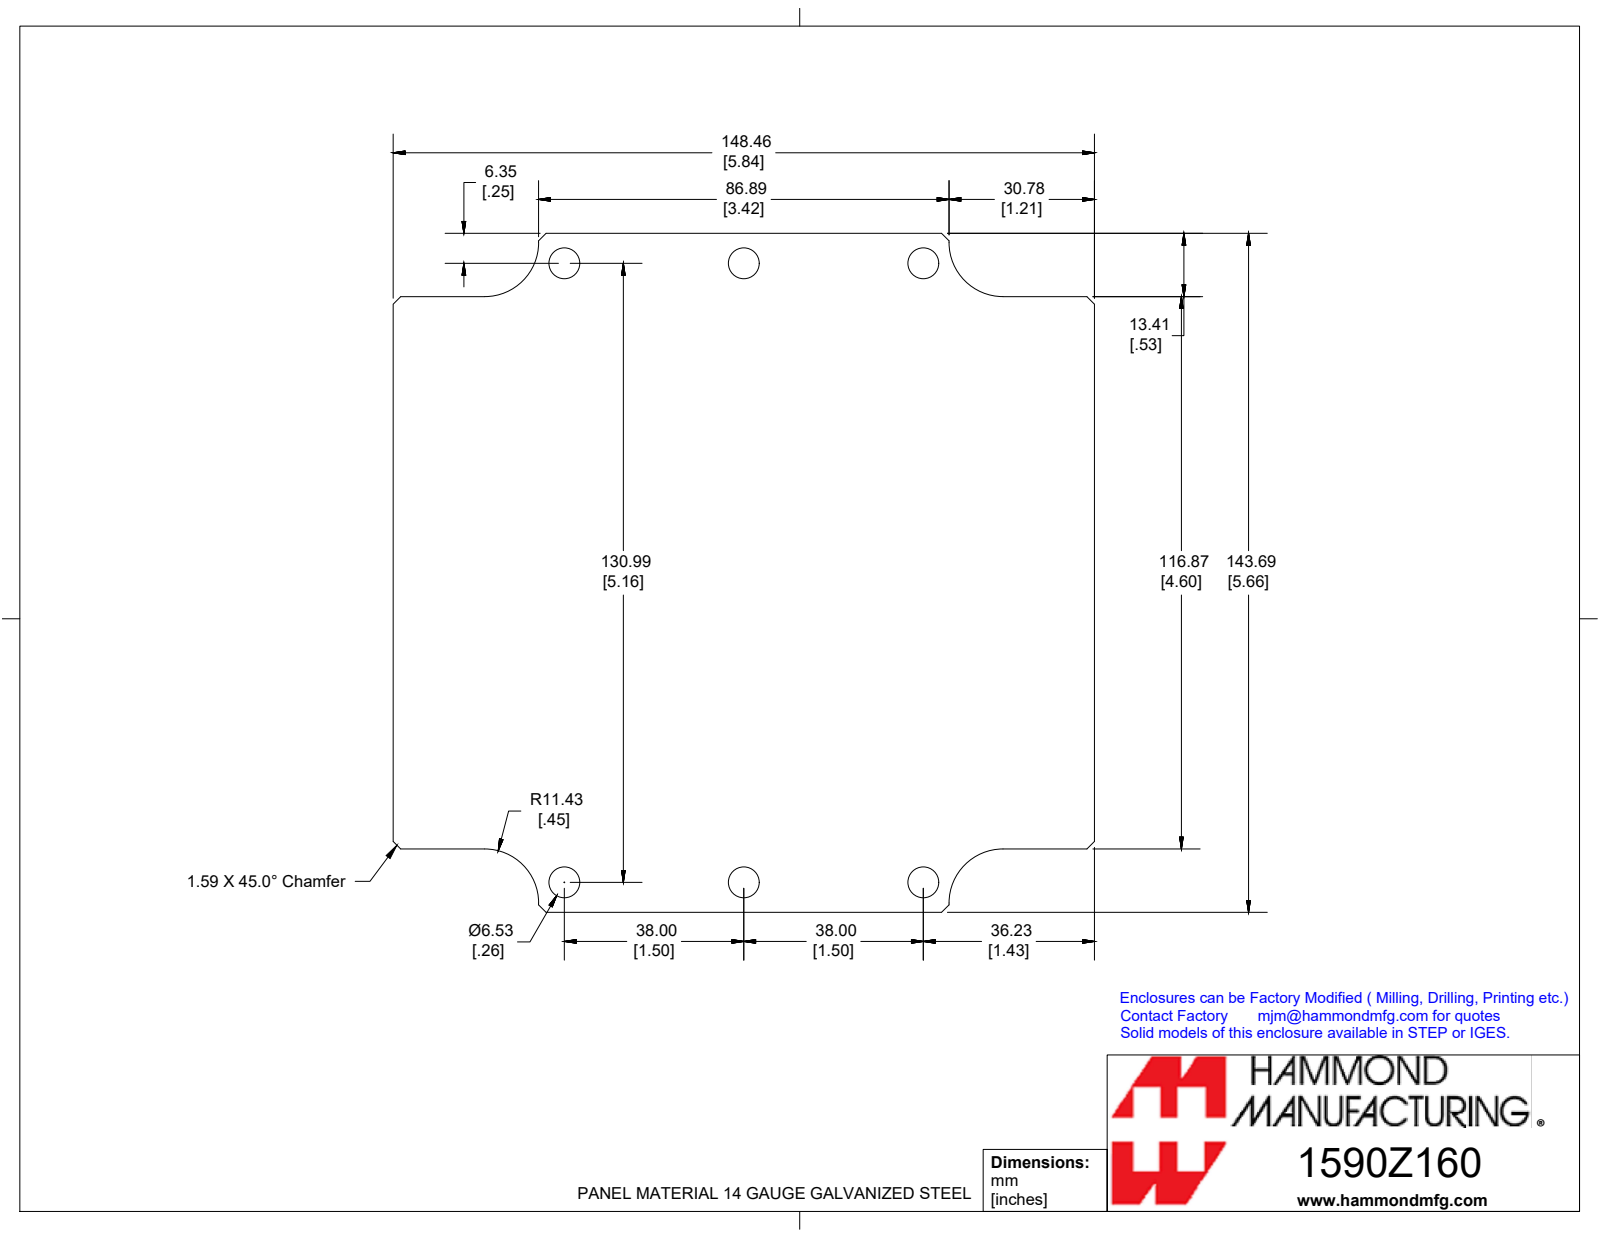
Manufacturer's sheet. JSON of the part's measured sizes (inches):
{"part_name": "1590Z160PL", "step_written_by": "SolidWorks 2019 (CONFIG_CONTROL_DESIGN)", "units": "inches", "bodies": {"solids": 1, "faces": 32, "planar": 22, "cylindrical": 10, "other": 0}, "overall_size": [5.845, 5.657, 0.064], "volume_in3": 1.927, "surface_area_in2": 62.41, "round_holes": [[0.257, 6]], "partial_cylinders_radius": [[0.45, 4]], "face_to_face_distances": [0.063, 5.845, 5.657, 0.528, 5.129, 4.601, 0.483, 6.813, 7.297, 6.33], "hole_center_spacings": [1.496, 5.369, 5.157, 2.992, 5.962]}
